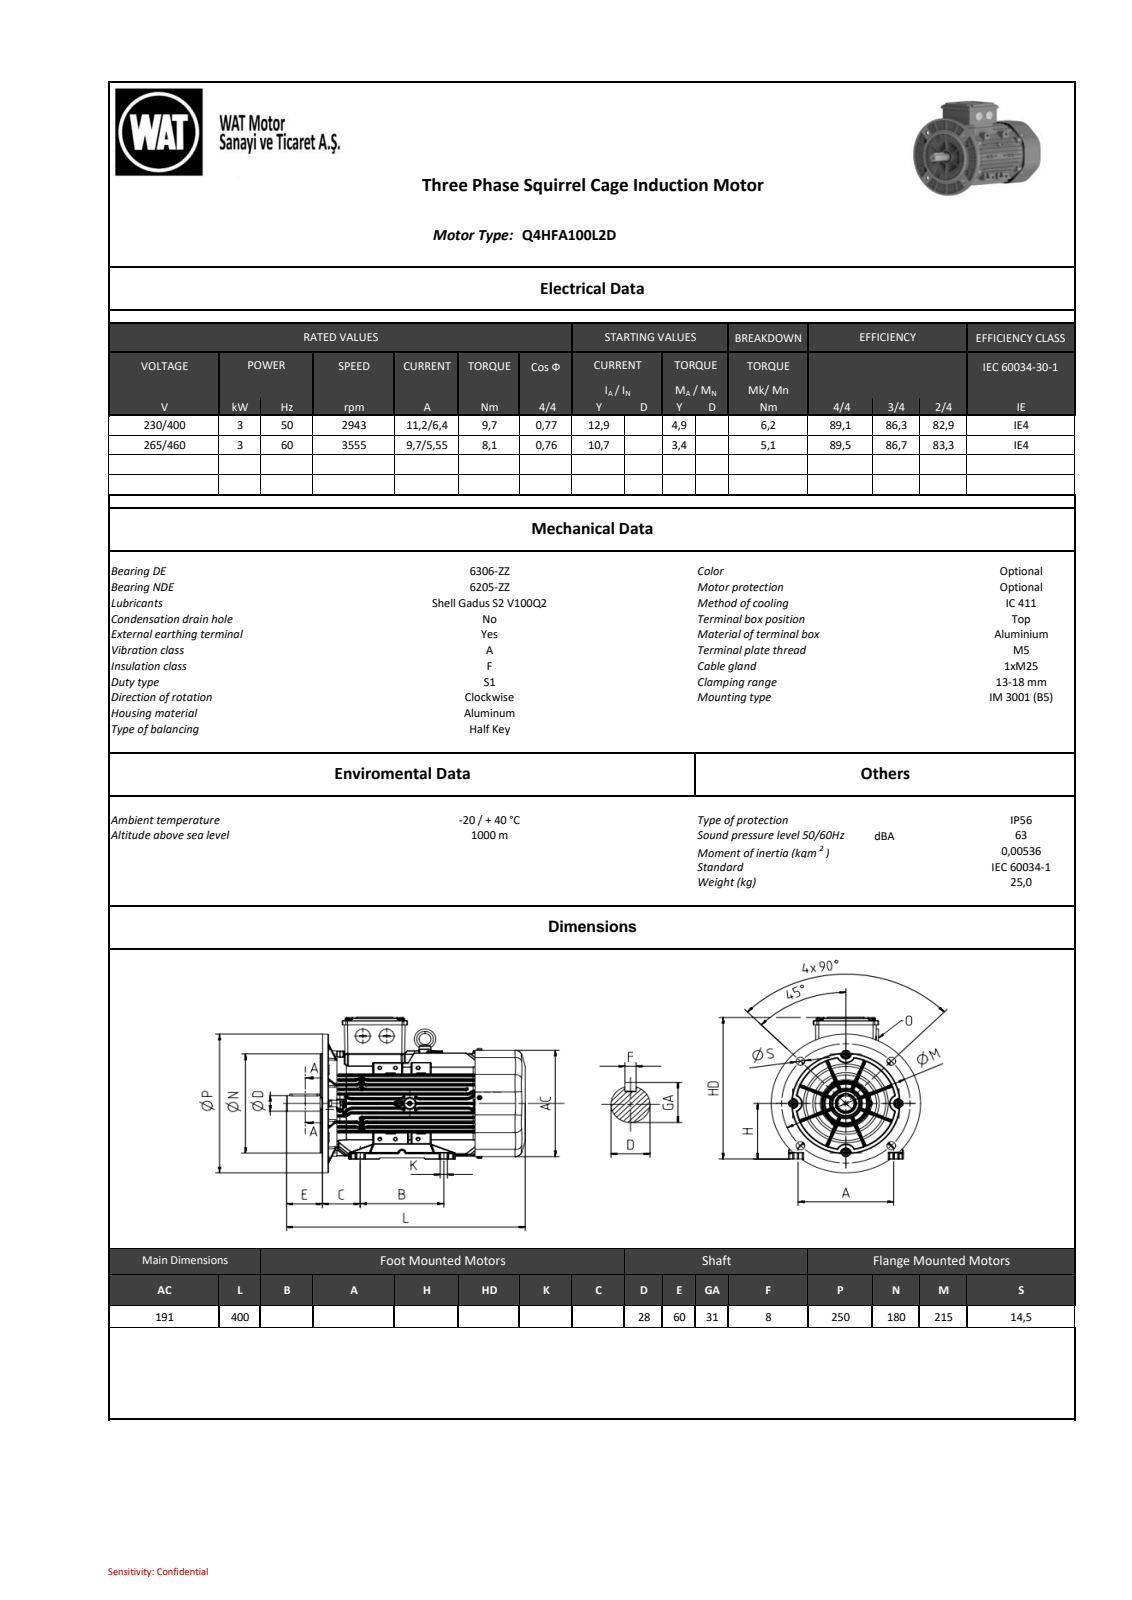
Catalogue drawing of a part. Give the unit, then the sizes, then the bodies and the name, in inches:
Units: inches
Overall size (bounding box): 15.721 × 11.05 × 9.84
Round holes (diameter × count): ⌀0.394 ×1, ⌀1.749 ×1, ⌀2.26 ×1, ⌀3.504 ×1, ⌀4.291 ×1, ⌀5.079 ×1, ⌀5.236 ×1
Round bosses / shafts (diameter × count): ⌀0.315 ×8, ⌀0.335 ×4, ⌀0.197 ×4, ⌀0.984 ×3, ⌀7.087 ×1, ⌀4.469 ×1, ⌀3.681 ×1, ⌀2.391 ×1
Partial cylindrical surfaces — rounded edges, fillets, slot ends (radius × count): R0.039 ×645, R0.031 ×536, R0.02 ×73, R0.098 ×62, R0.079 ×60, R0.032 ×48, R0.197 ×40, R0.591 ×26
Main face-to-face distances: 0.336, 0.333, 0.333, 3.002, 0.666, 3.679, 1.007, 0.671, 3.019, 2.348
Bodies: 0 solids, 5847 faces (1213 planar, 2204 cylindrical, 2430 other)
Part name (STEP PRODUCT): QH series_ 100_B5_stp_objects
STEP written by: SIEMENS PLM Software NX2206.8101 (AUTOMOTIVE_DESIGN)
